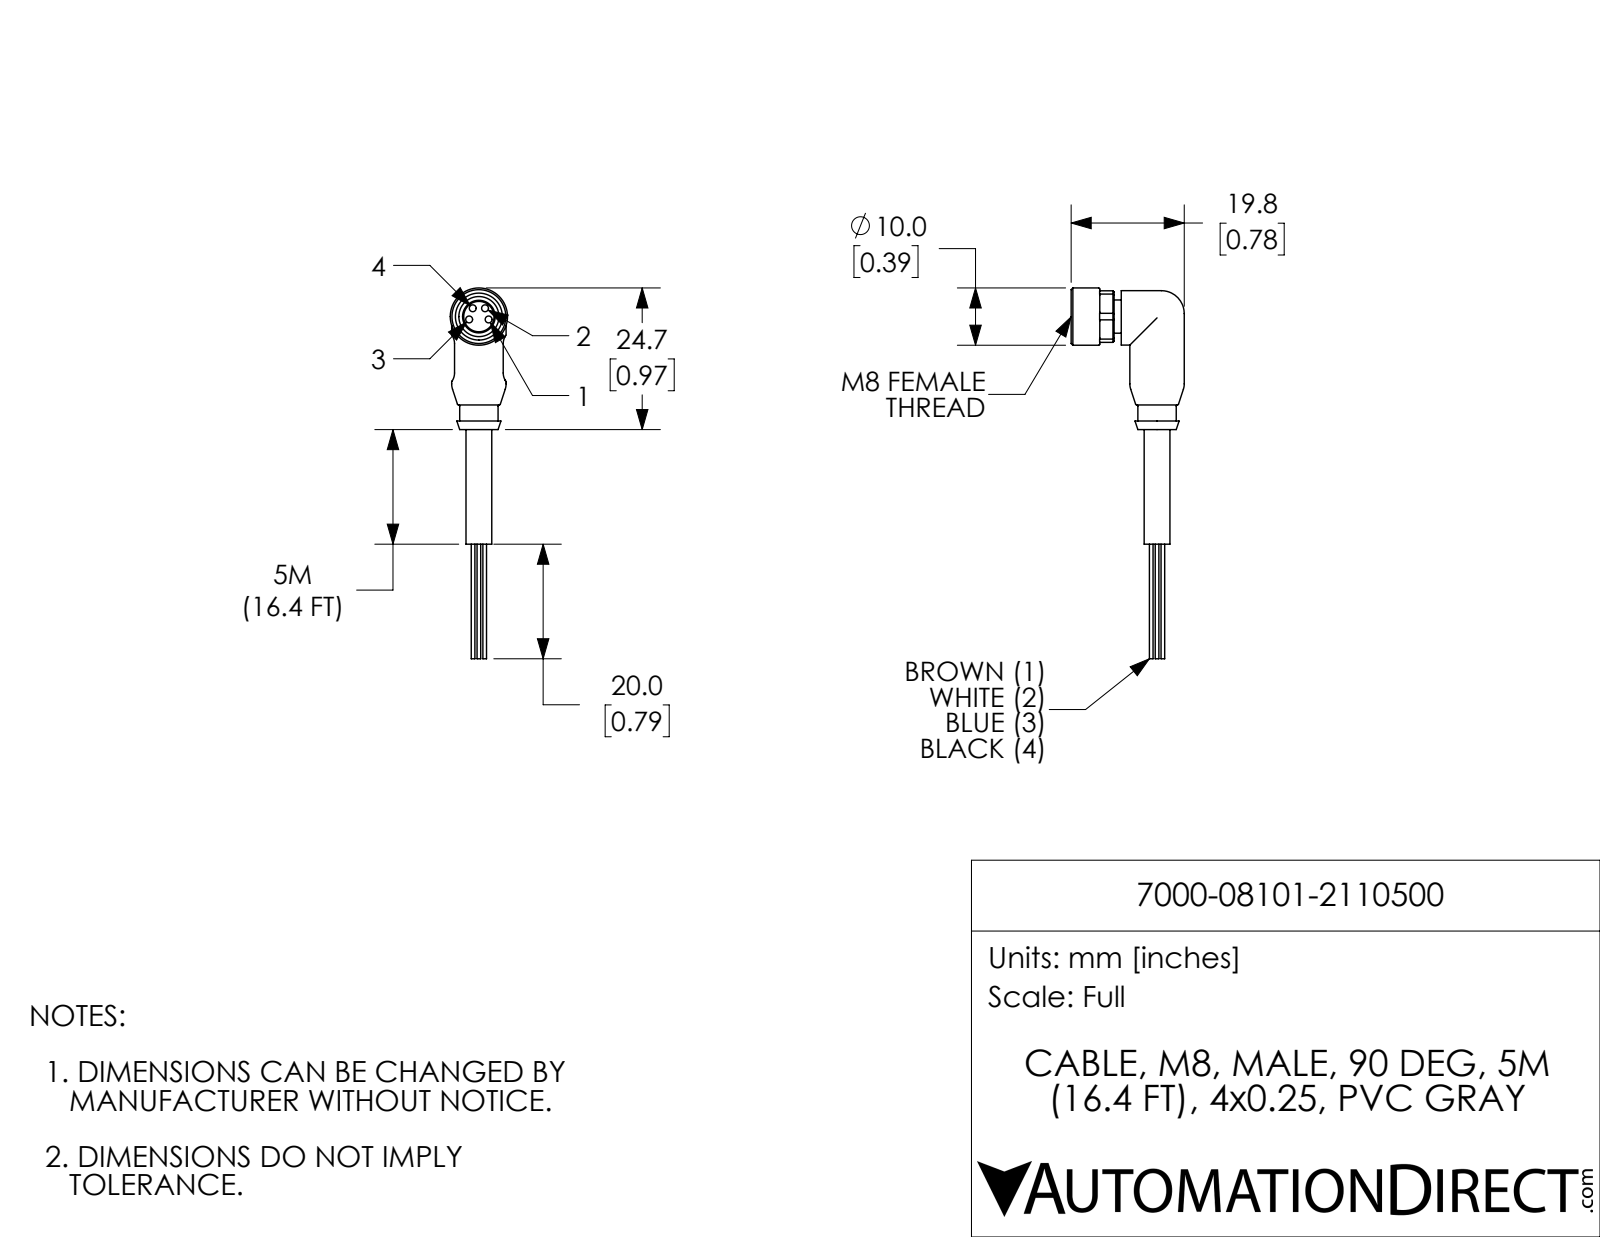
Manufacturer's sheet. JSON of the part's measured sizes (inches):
{"part_name": "7000-08101-2110500", "step_written_by": "SolidWorks 2017 (AUTOMOTIVE_DESIGN)", "units": "inches", "bodies": {"solids": 5, "faces": 117, "planar": 41, "cylindrical": 47, "other": 29}, "overall_size": [2.548, 0.778, 0.394], "volume_in3": 0.147, "surface_area_in2": 2.976, "round_holes": [[0.047, 4], [0.276, 1]], "round_bosses_or_shafts": [[0.025, 3], [0.374, 2], [0.394, 1], [0.264, 1], [0.228, 1], [0.224, 1], [0.177, 1], [0.025, 1]], "partial_cylinders_radius": [[0.008, 4], [0.098, 4], [0.193, 1]], "face_to_face_distances": [0.049, 0.354, 0.059, 0.335, 0.028, 0.787, 0.268, 0.317, 0.295, 0.344], "hole_center_spacings": [0.07, 0.071, 0.081, 0.133, 0.084, 0.134]}
